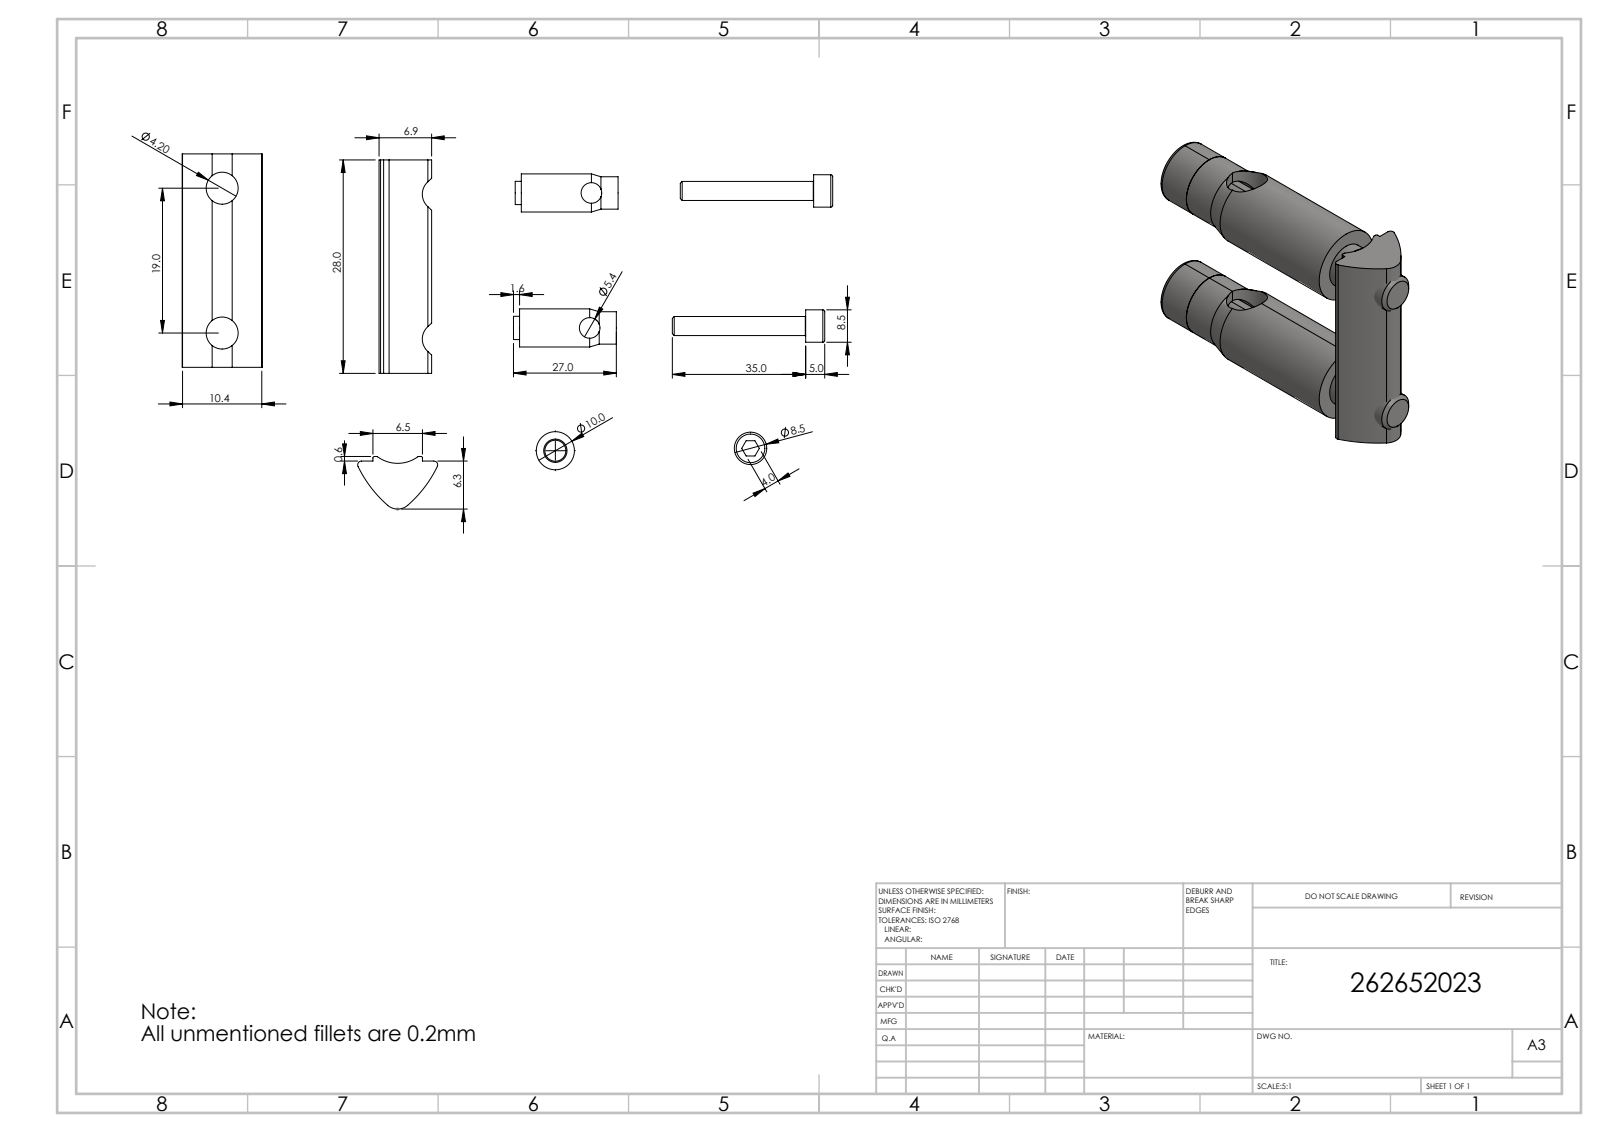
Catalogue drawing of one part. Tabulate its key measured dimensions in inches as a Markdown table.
| quantity | value |
| --- | --- |
| part name | 262652023_Automatik-Combiverbinder_Nut6_30_Shrinkwrap_1 |
| STEP written by | Autodesk Inventor 2019 (AUTOMOTIVE_DESIGN) |
| units | inches |
| bodies | 5 solids, 78 faces (32 planar, 30 cylindrical, 16 other) |
| overall size | 1.575 × 1.142 × 0.413 |
| volume | 0.323 in³ |
| surface area | 8.226 in² |
| round holes (diameter × count) | 0.165 × 2, 0.217 × 2, 0.213 × 1 |
| round bosses / shafts (diameter × count) | 0.394 × 2, 0.335 × 2, 0.241 × 2, 0.197 × 2 |
| partial cylindrical surfaces (radius × count) | 0.008 × 4, 0.02 × 2, 0.63 × 2, 0.079 × 1, 0.177 × 1 |
| main face-to-face distances | 1, 1.118, 0.118, 0.197, 1.197, 1.315, 1.102, 0.157, 1.575, 1.378 |
| hole center spacings | 0.748 |
